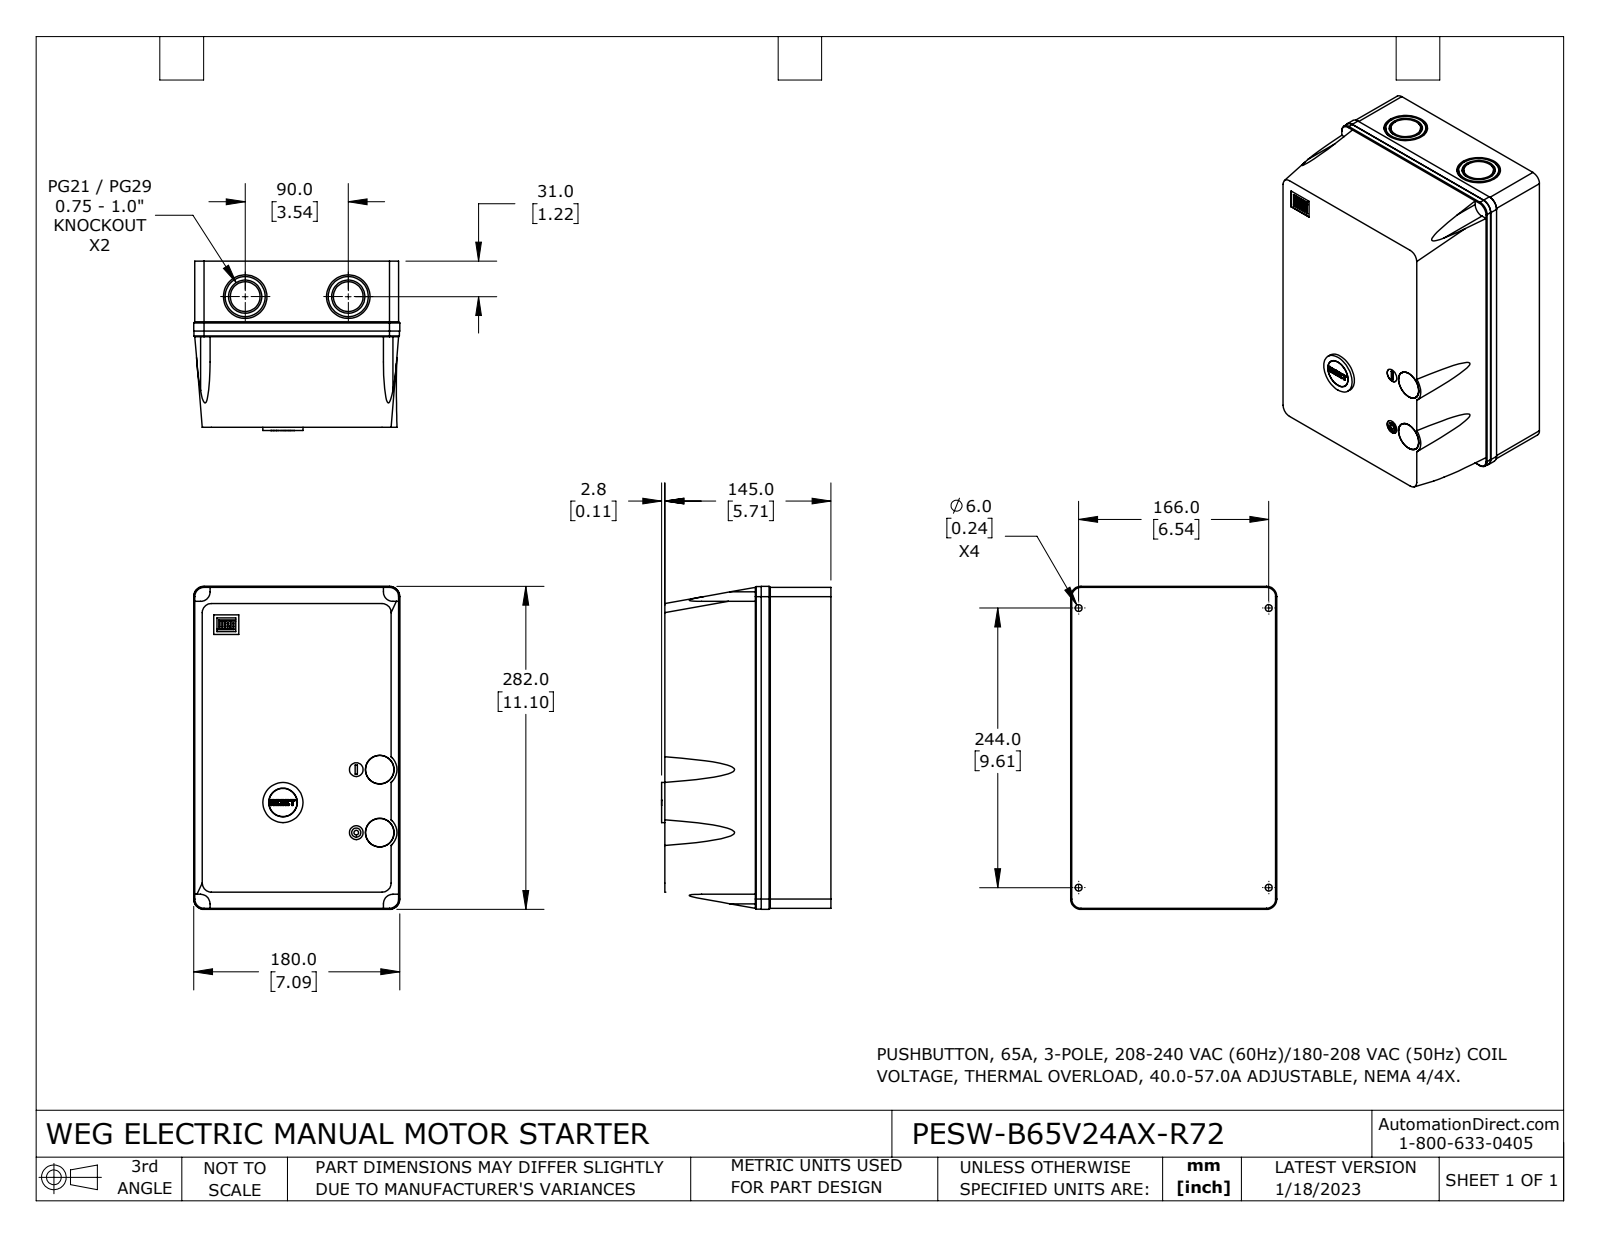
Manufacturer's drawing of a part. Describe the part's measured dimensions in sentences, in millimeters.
The part is named "PESW-B65V24AX-R72". Its 3-D file was written by "SolidWorks 2021 (CONFIG_CONTROL_DESIGN)". It is 3 solids with 286 faces: 130 planar, 144 cylindrical and 12 other. Overall it measures 282 by 180 by 147.9 millimeters. Its volume is 7 014 000 cubic millimeters and its surface area 232 257 square millimeters. Round holes: 4 of diameter 6, 3 of diameter 25, 2 of diameter 12, 2 of diameter 29, 2 of diameter 38, 1 of diameter 4, 1 of diameter 30.5. Round bosses or shafts: 3 of diameter 35, 2 of diameter 26, 2 of diameter 24.8, 1 of diameter 30.3, 1 of diameter 24.6, 1 of diameter 14, 1 of diameter 8. Partial cylindrical surfaces (rounded edges, fillets, slot ends): 34 of radius 0.1, 4 of radius 8, 4 of radius 8.3, 4 of radius 8.7, 4 of radius 9, 1 of radius 1.6. The main face-to-face distances are 145, 178, 280, 1, 0.7, 179, 179.7, 178.7, 281, 180. The hole center spacings are 20.5, 55, 58.7, 166, 244, 295.11, 49.14, 57.14.
